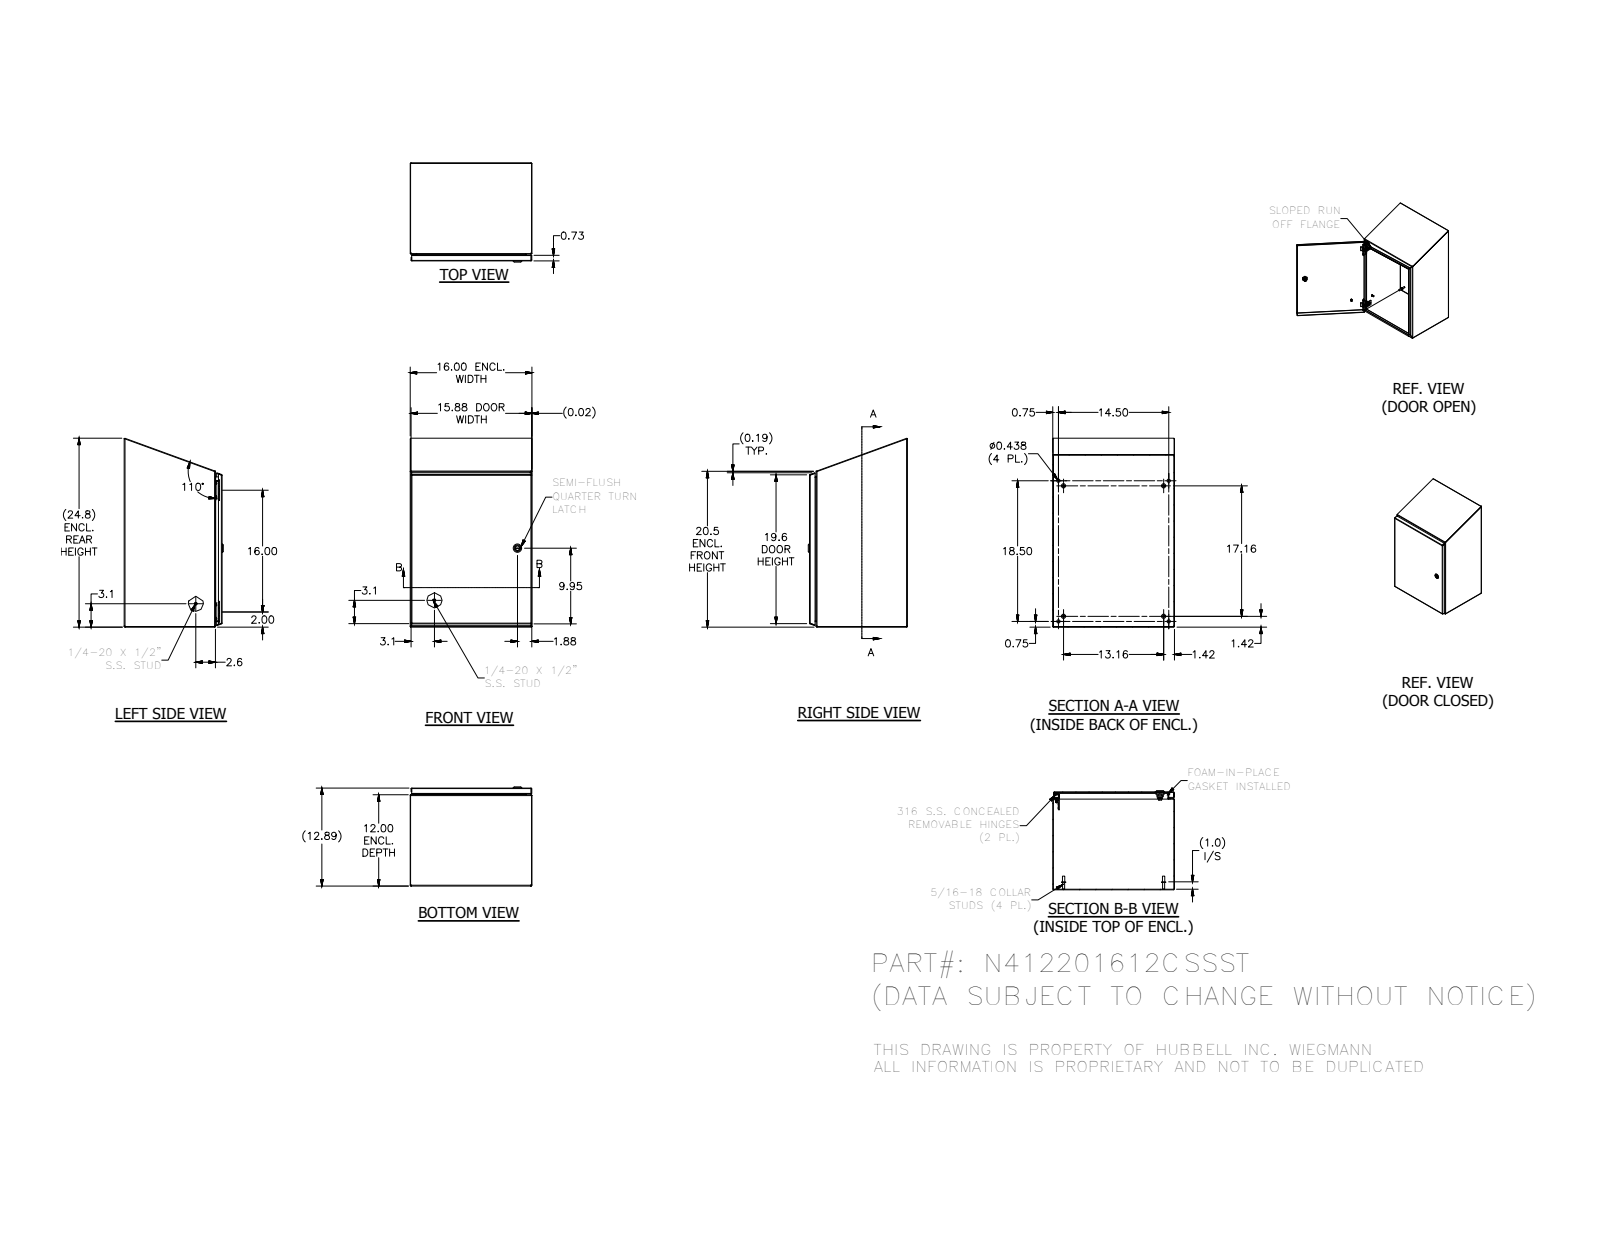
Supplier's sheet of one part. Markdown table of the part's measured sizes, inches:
| quantity | value |
| --- | --- |
| part name | N412201612CSSST |
| STEP written by | SolidWorks 2018 (AUTOMOTIVE_DESIGN) |
| units | inches |
| bodies | 36 solids, 1426 faces (538 planar, 509 cylindrical, 379 other) |
| overall size | 24.847 × 16 × 13.044 |
| volume | 133.9 in³ |
| surface area | 3 641 in² |
| round holes (diameter × count) | 0.093 × 4, 0.152 × 4, 0.167 × 4, 0.172 × 4, 0.187 × 4, 0.437 × 4, 0.156 × 3, 0.187 × 1, 0.197 × 1, 0.315 × 1, 0.394 × 1, 0.402 × 1 |
| round bosses / shafts (diameter × count) | 0.25 × 10, 0.563 × 4, 0.36 × 4, 0.32 × 4, 0.3 × 4, 0.275 × 4, 0.256 × 4, 0.164 × 4 |
| partial cylindrical surfaces (radius × count) | 0.031 × 29, 0.05 × 26, 0.105 × 19, 0.016 × 18, 0.02 × 16, 0.125 × 16, 0.032 × 8, 0.524 × 6 |
| main face-to-face distances | 0.074, 12.813, 15.926, 12.739, 12.887, 16, 15.852, 11.926, 0.887, 0.813 |
| hole center spacings | 16, 14.774, 0.5, 0.656, 0.66, 0.952, 1.307, 1.311 |
